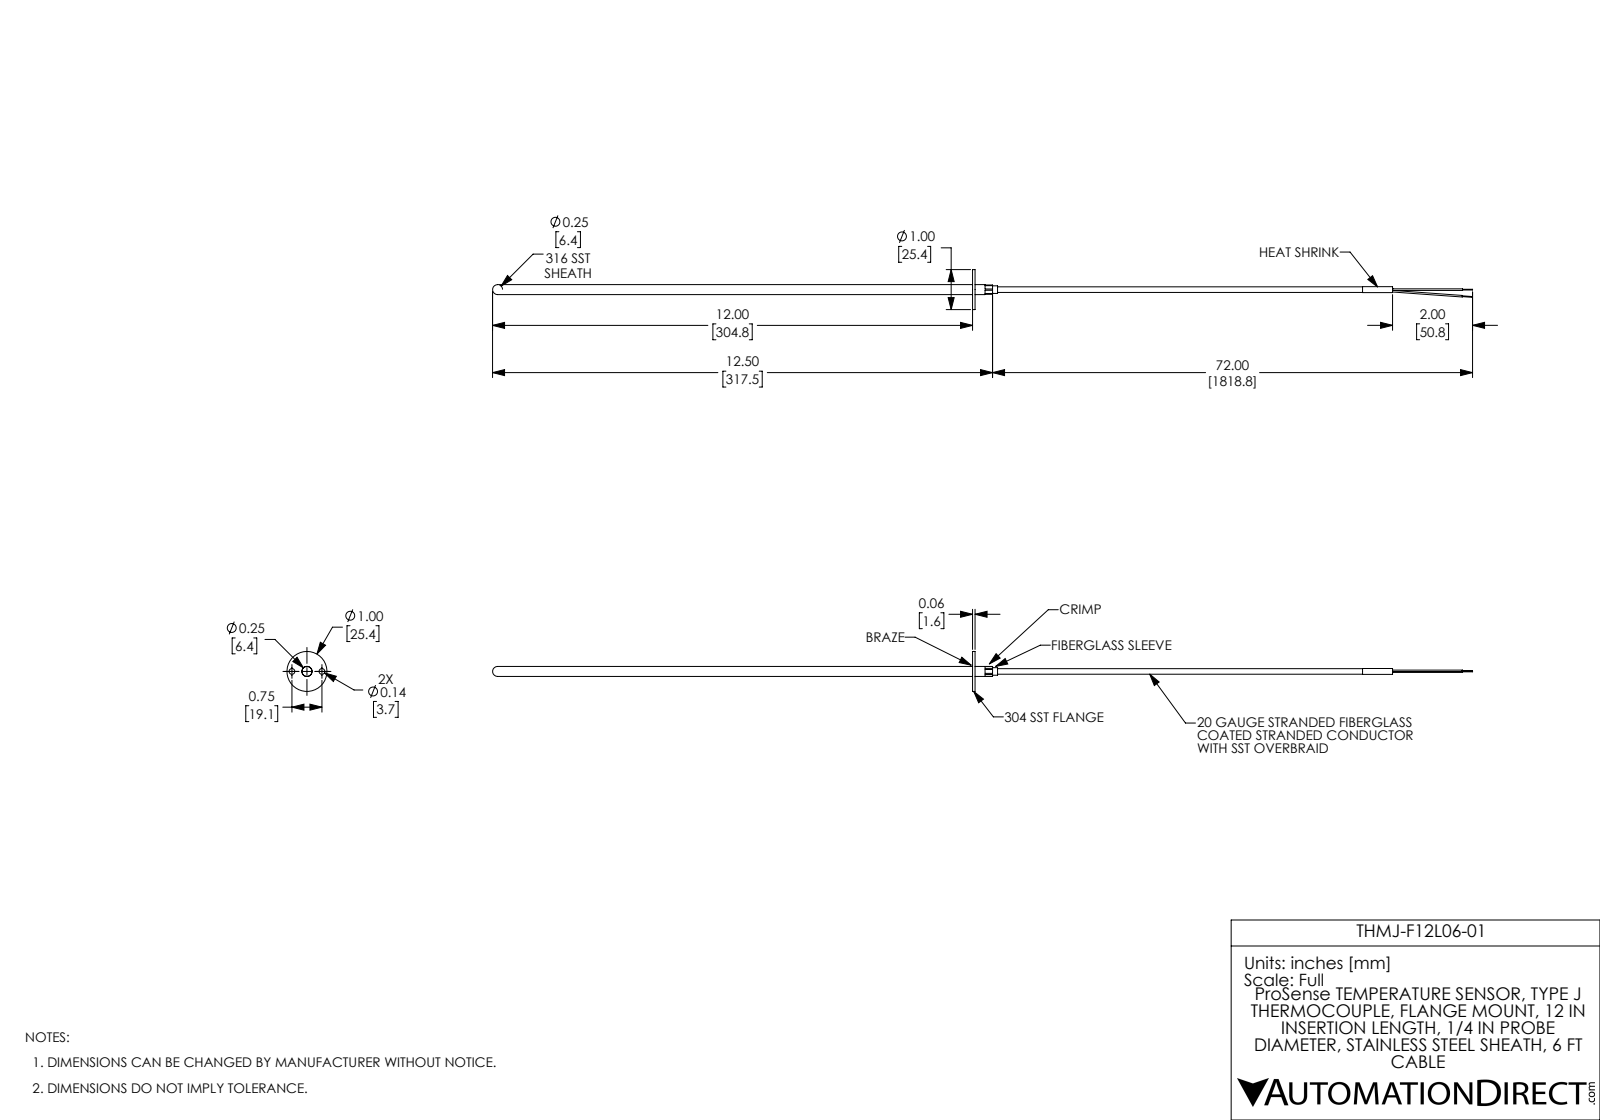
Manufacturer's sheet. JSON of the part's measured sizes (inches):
{"part_name": "THMJ-F12L06-01", "step_written_by": "SolidWorks 2017 (AUTOMOTIVE_DESIGN)", "units": "inches", "bodies": {"solids": 7, "faces": 65, "planar": 30, "cylindrical": 32, "other": 3}, "overall_size": [24.5, 1, 1], "volume_in3": 0.826, "surface_area_in2": 26.97, "round_holes": [[0.144, 3], [0.136, 1], [0.189, 1], [0.257, 1]], "round_bosses_or_shafts": [[1, 1], [0.25, 1], [0.19, 1], [0.188, 1], [0.148, 1], [0.14, 1], [0.132, 1], [0.04, 1]], "face_to_face_distances": [0.063, 0.5, 0.437, 0.231, 0.75, 0.125, 0.188, 0.625, 0.625, 0.562], "hole_center_spacings": [0.375, 0.375, 0.75]}
